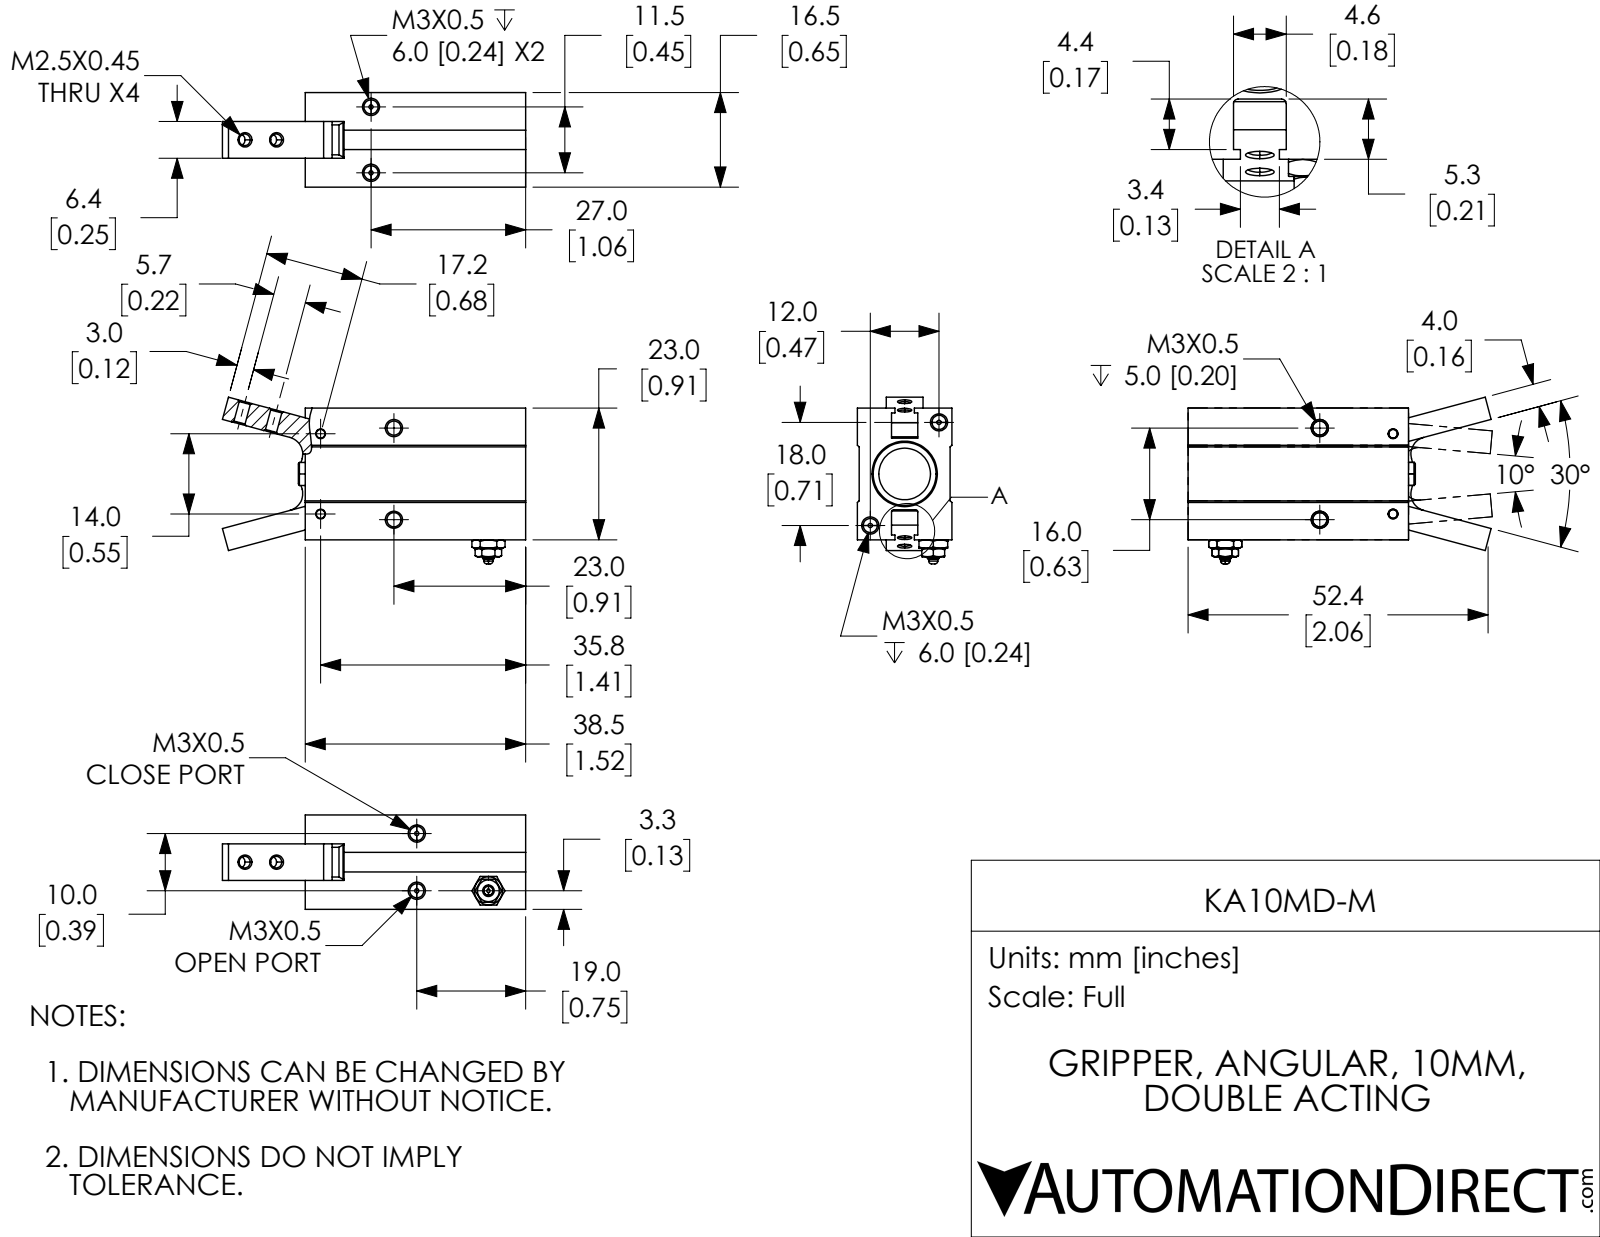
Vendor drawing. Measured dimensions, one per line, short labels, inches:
name: KA10MD-M-4; KA10MD-M-1; KA10MD-M-2; KA10MD-M-3 (+1 more)
written by: SolidWorks 2017 (AUTOMOTIVE_DESIGN)
unit: in
bodies: 4 solids, 262 faces (100 planar, 86 cylindrical, 76 other)
size: 2.084 × 1.145 × 0.65
volume: 0.718 in³; area: 12.92 in²
holes: 4× ⌀0.097, 4× ⌀0.097, 3× ⌀0.059, 2× ⌀0.079, 2× ⌀0.079, 2× ⌀0.126, 1× ⌀0.236, 1× ⌀0.354, 1× ⌀0.394, 1× ⌀0.433, 1× ⌀0.472
bosses: 1× ⌀0.39, 1× ⌀0.205, 1× ⌀0.157, 1× ⌀0.079, 1× ⌀0.063
rounds: 2× R0.016, 2× R0.079, 2× R0.118
face distances: 0.638, 0.222, 0.234, 0.415, 0.404, 0.217, 0.439, 0.65, 0.199, 0.451
hole spacings: 0.224, 0.285, 0.317, 0.426, 0.506, 0.528, 0.659, 0.776
